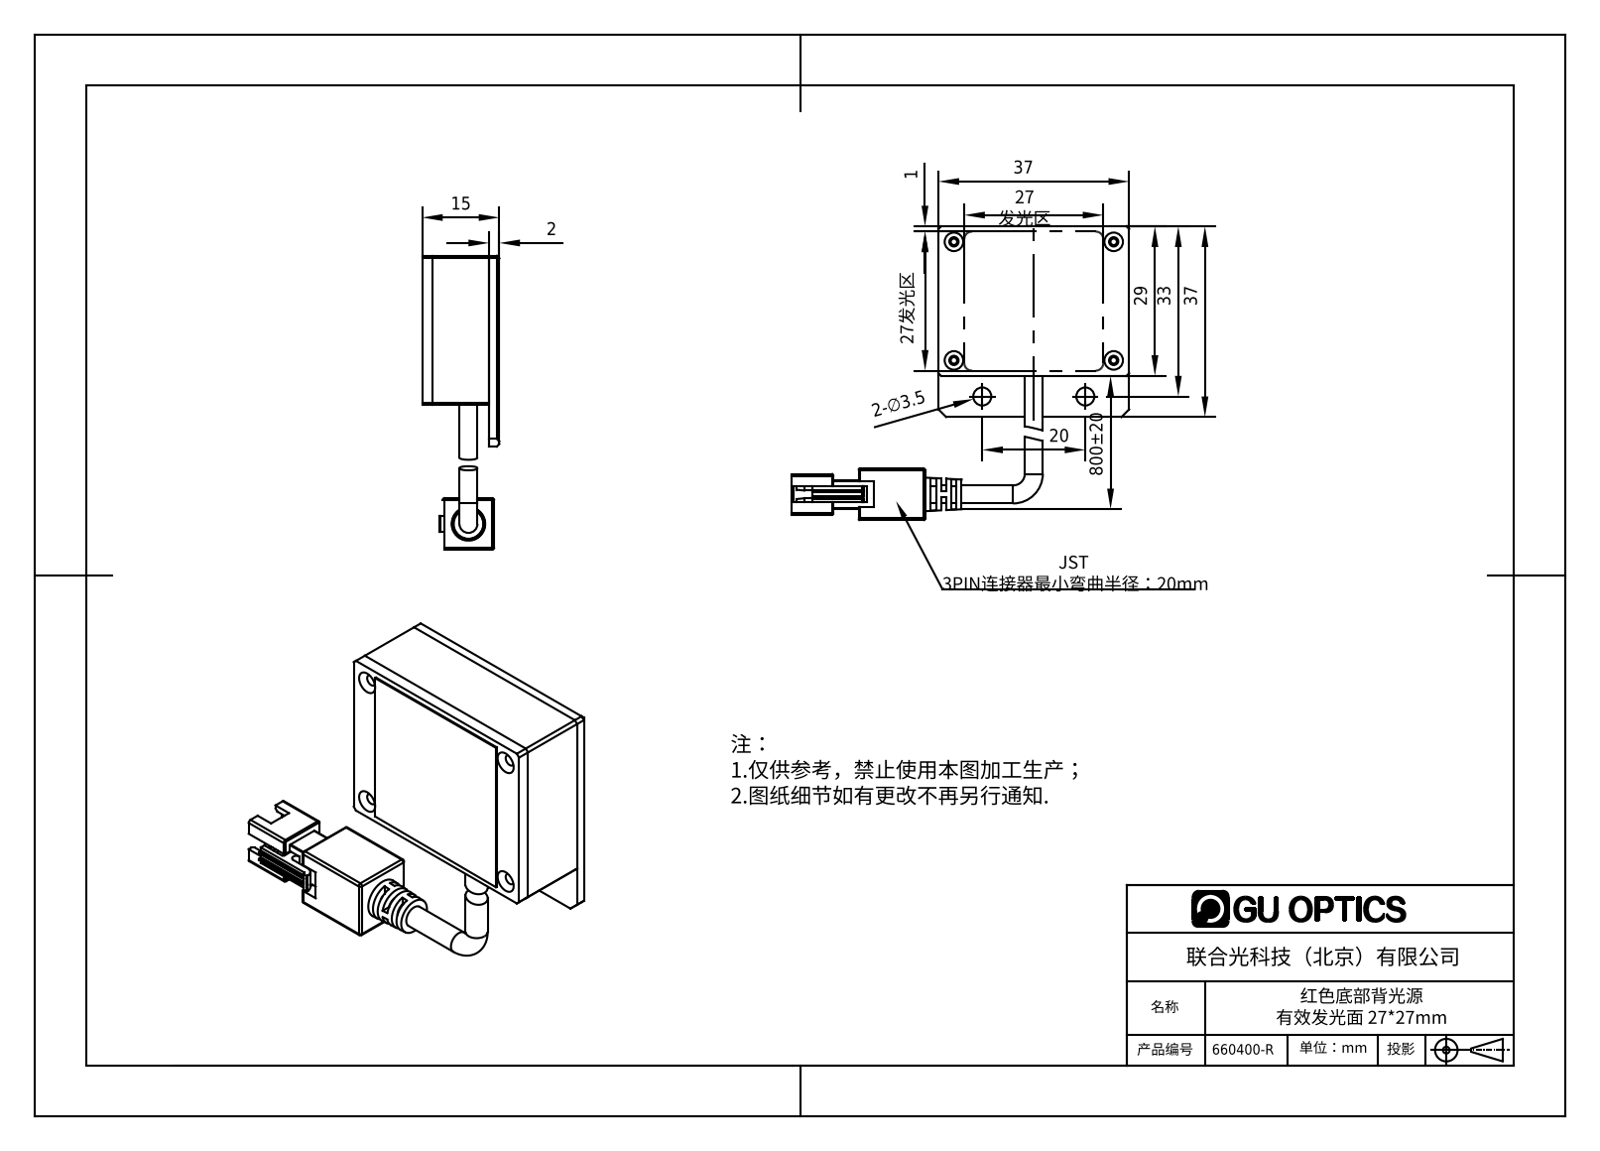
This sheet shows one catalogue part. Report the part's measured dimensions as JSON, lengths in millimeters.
{"part_name": "红色底部背光源 有效发光面 2727mm", "step_written_by": "SolidWorks 2016 (AUTOMOTIVE_DESIGN)", "units": "millimeters", "bodies": {"solids": 6, "faces": 616, "planar": 375, "cylindrical": 122, "other": 119}, "overall_size": [65.5, 57, 15.2], "volume_mm3": 11682, "surface_area_mm2": 12966, "round_holes": [[1.25, 4], [1.6, 4], [1.8, 4], [2, 4], [2.4, 4], [3.5, 2]], "round_bosses_or_shafts": [[3.5, 2]], "partial_cylinders_radius": [[0.1, 15], [0.2, 13], [0.4, 12], [1, 4], [1.5, 4], [0.75, 2], [0.8, 2], [0.3, 1]], "face_to_face_distances": [2, 1, 11, 13, 2.3, 10.7, 1.3, 28, 2.2, 15.2], "hole_center_spacings": [8.9, 23, 26.44, 30.5, 31, 38.6, 39.37, 20]}
